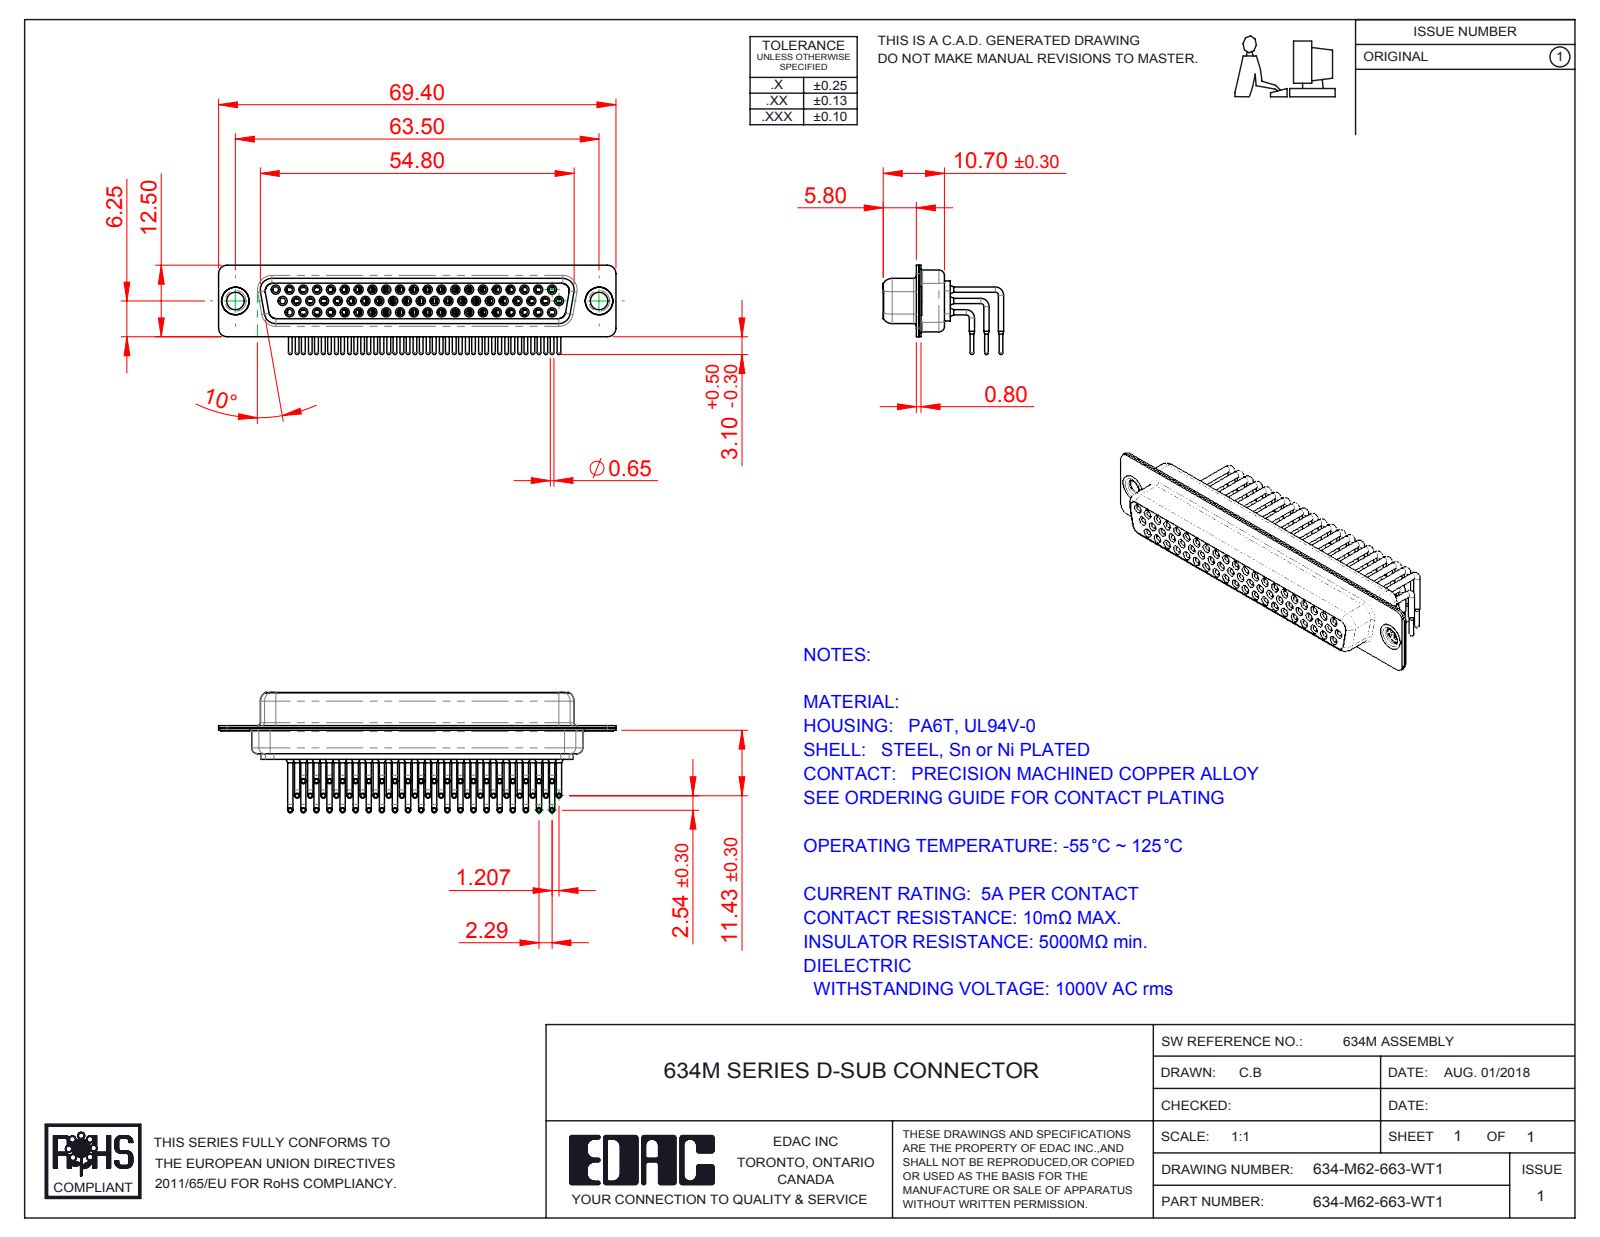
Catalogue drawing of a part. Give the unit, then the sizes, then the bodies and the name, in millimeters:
Units: millimetres
Overall size (bounding box): 69.4 × 21.02 × 15.6
Round holes (diameter × count): ⌀1 ×62, ⌀1.1 ×62, ⌀1.7 ×62, ⌀1.8 ×62, ⌀2 ×62, ⌀3.05 ×2, ⌀4 ×2, ⌀4.8 ×2
Round bosses / shafts (diameter × count): ⌀0.9 ×124, ⌀1.6 ×62, ⌀1.5 ×62, ⌀0.65 ×62, ⌀2 ×56, ⌀5 ×2, ⌀4.9 ×2, ⌀3.55 ×2
Partial cylindrical surfaces — rounded edges, fillets, slot ends (radius × count): R1.5 ×16, R2 ×12, R1.35 ×8, R1.6 ×8, R0.25 ×4, R0.5 ×4, R0.6 ×4, R0.65 ×4
Main face-to-face distances: 0.4, 1.45, 8.95, 1.9, 8.5, 2.3, 6.2, 0.45, 7.05, 0.85
Hole centre spacings: 7.24, 2.32, 2.41, 9.65, 4.13, 4.83, 16.89, 14.48
Volume: 5 326 mm³ · Surface area: 17 717 mm²
Bodies: 67 solids, 3539 faces (997 planar, 1547 cylindrical, 995 other)
Part name (STEP PRODUCT): 634M Contact Row 2; 634M Contact Row 3; 634M Contact Row 1; 634-M62-663-WT1 (+4 more)
STEP written by: SolidWorks 2016 (CONFIG_CONTROL_DESIGN)
